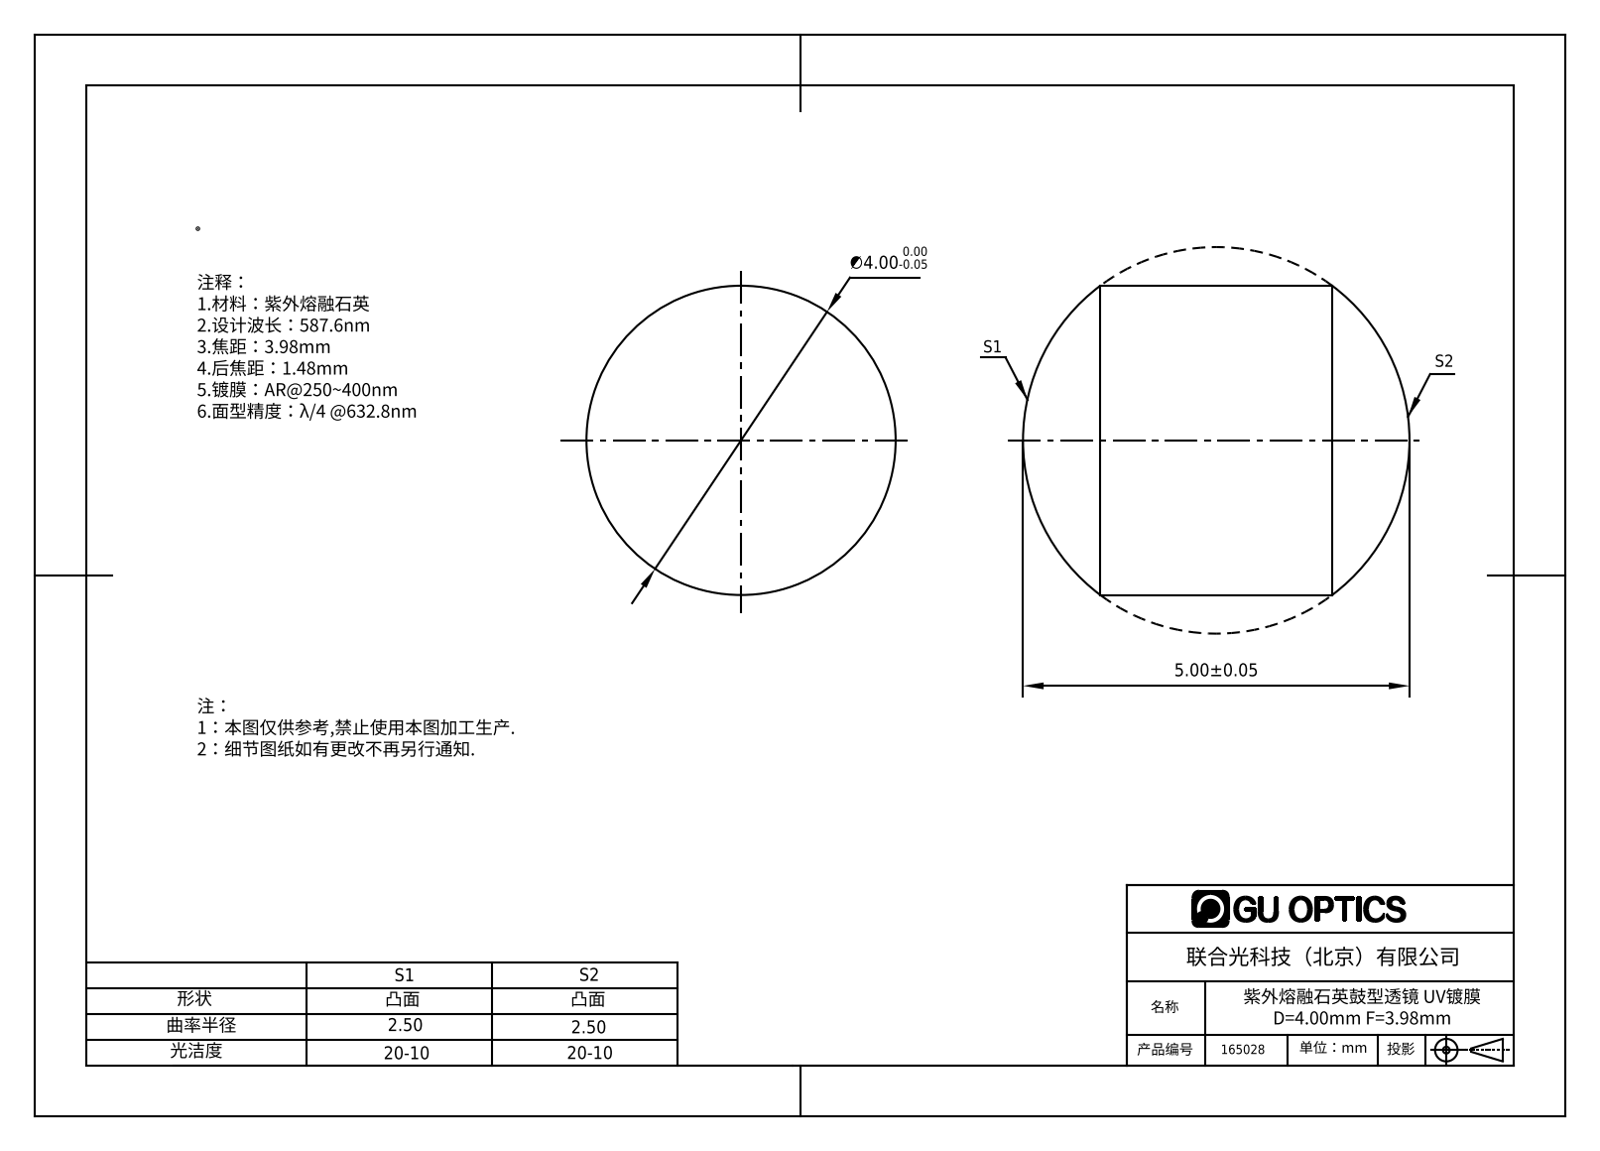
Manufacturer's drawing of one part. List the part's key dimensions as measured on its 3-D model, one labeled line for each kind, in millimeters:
Part name (STEP PRODUCT): 165003
STEP written by: SolidWorks 2016 (CONFIG_CONTROL_DESIGN)
Units: millimetres
Bodies: 1 solid, 6 faces (0 planar, 2 cylindrical, 4 other)
Overall size (bounding box): 74.99 × 59.99 × 59.99
Volume: 173 128 mm³ · Surface area: 15 548 mm²
Round bosses / shafts (diameter × count): ⌀59.99 ×1
